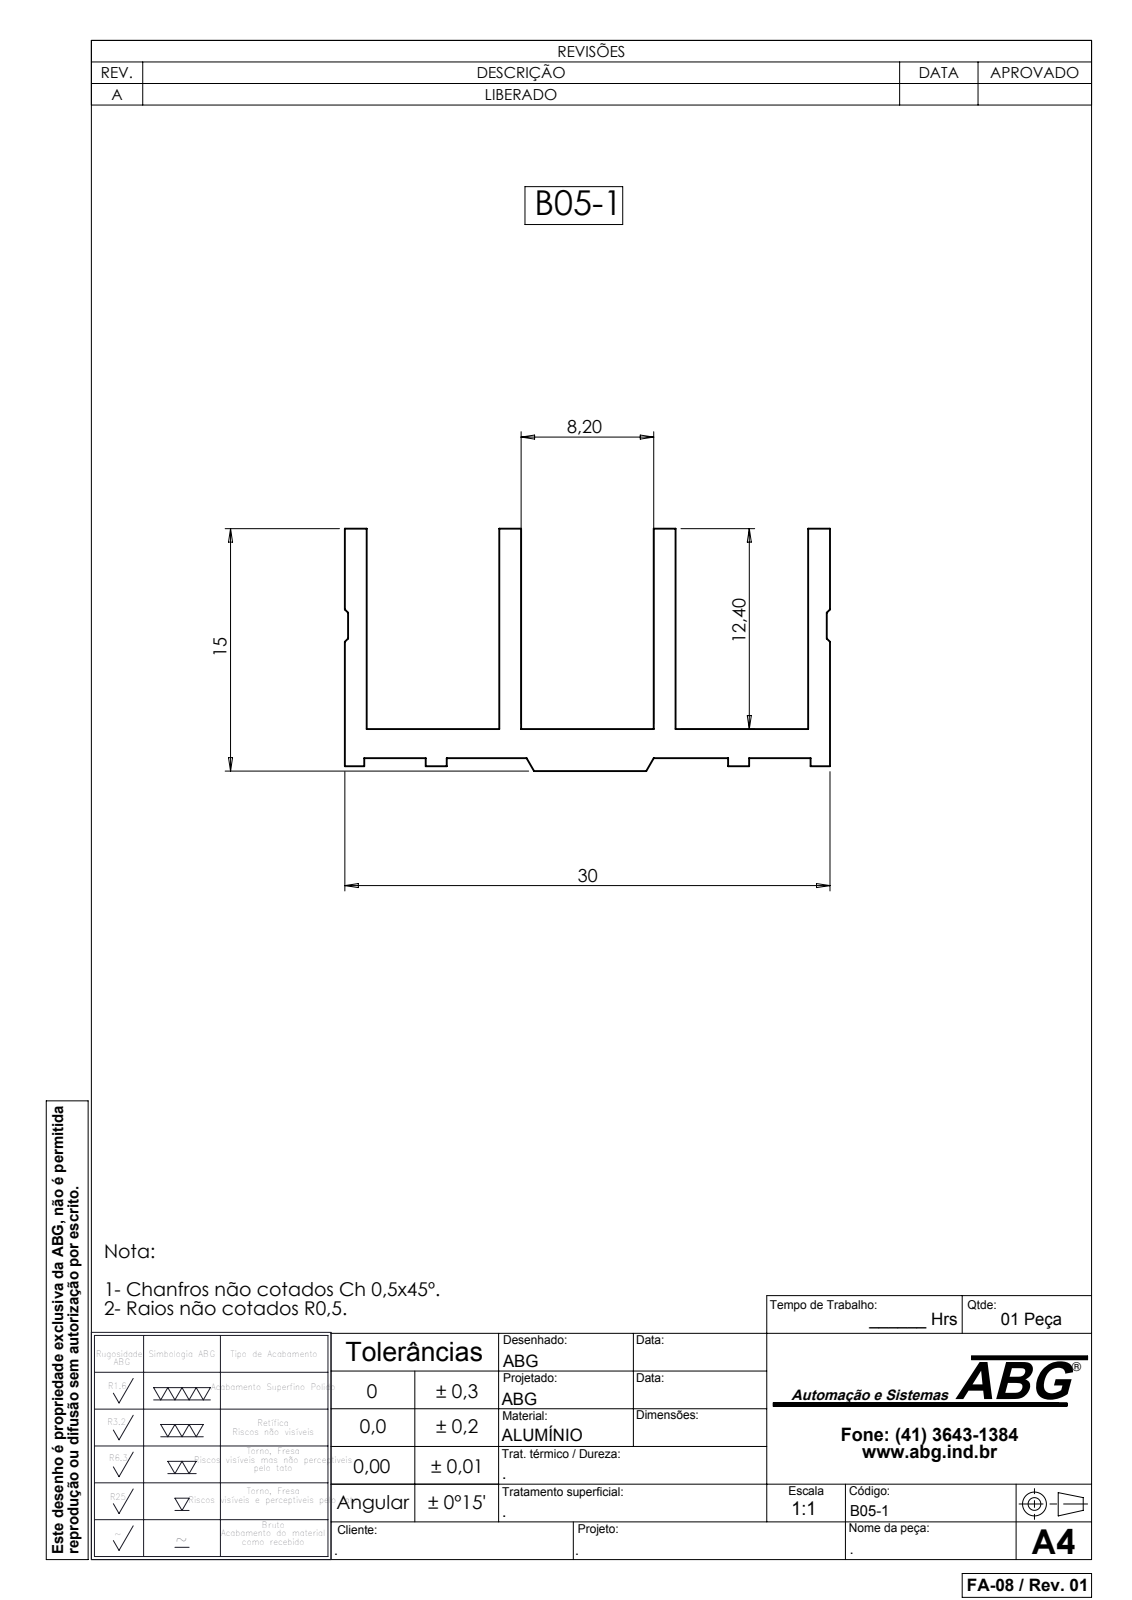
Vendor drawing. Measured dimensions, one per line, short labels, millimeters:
name: B05-1
written by: SolidWorks 2007 (CONFIG_CONTROL_DESIGN)
unit: mm
bodies: 1 solid, 42 faces (42 planar, 0 cylindrical, 0 other)
size: 3000 × 30 × 15
volume: 385 980 mm³; area: 504 423 mm²
face distances: 9.55, 19.1, 1.35, 10.9, 8.2, 20.45, 28.65, 17.75, 1.8, 30
